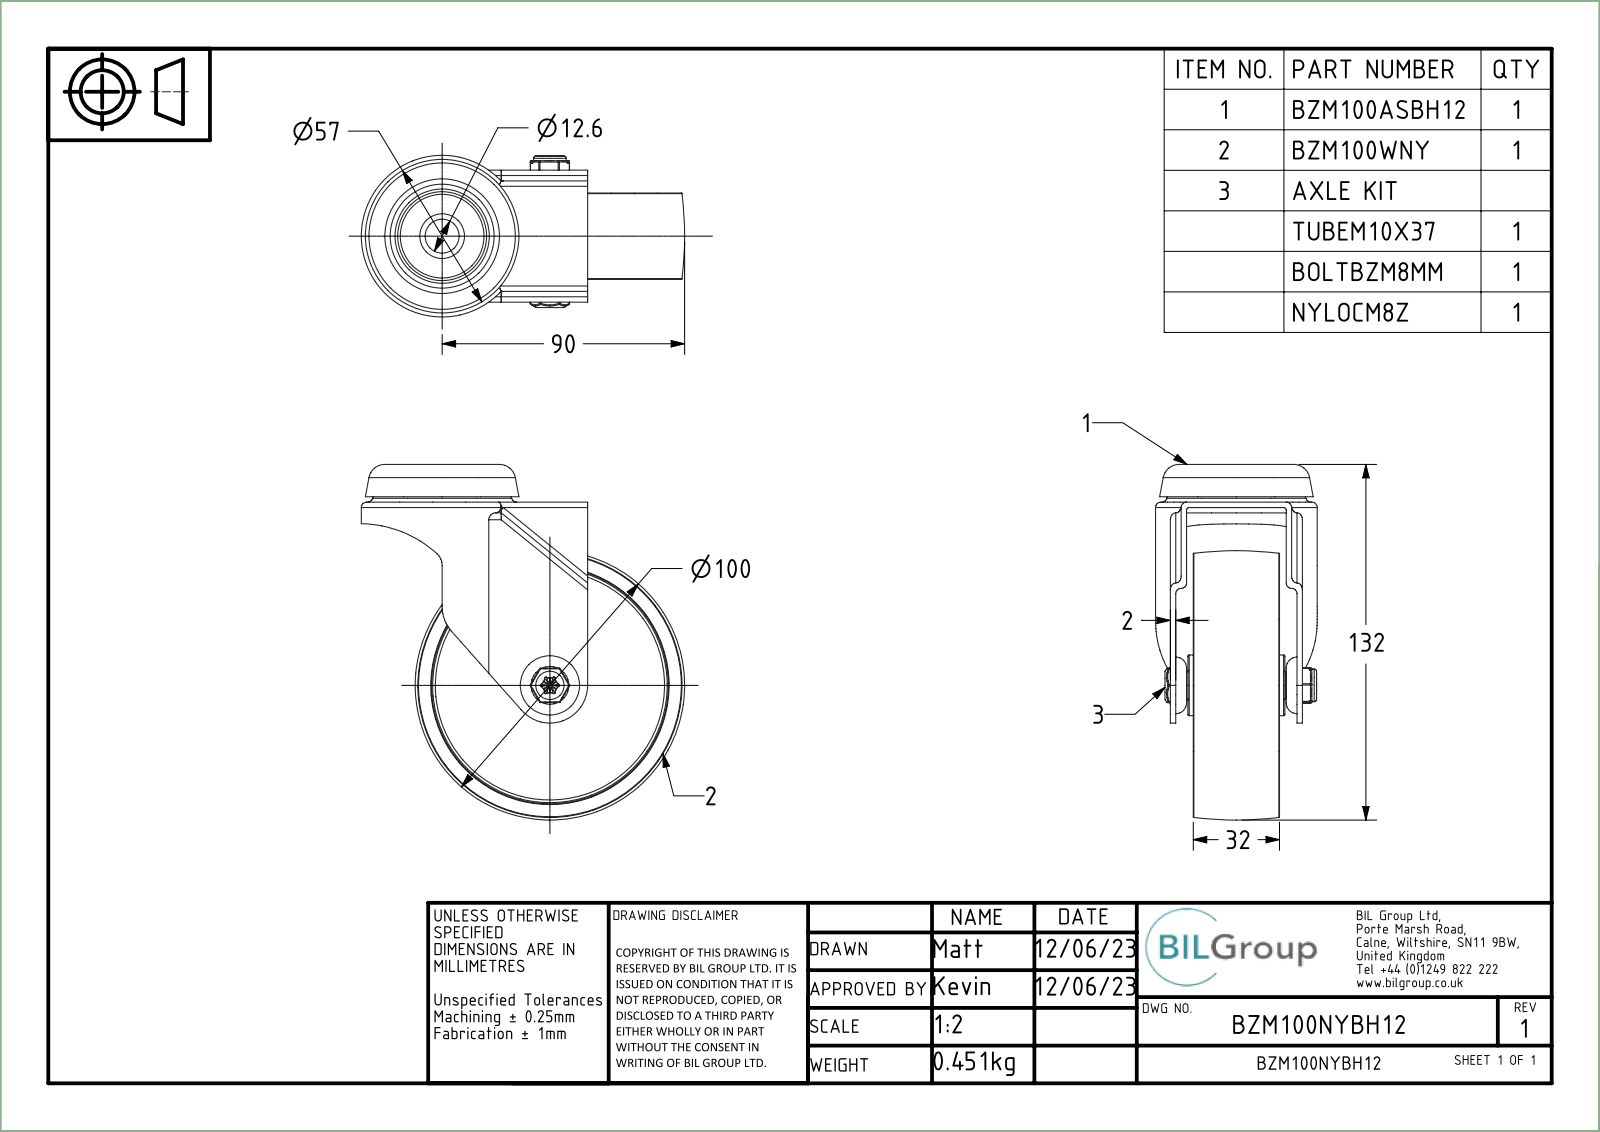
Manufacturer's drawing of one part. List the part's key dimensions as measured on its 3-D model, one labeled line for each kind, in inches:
Part name (STEP PRODUCT): BZM100ASBH12; ZINC PLATED PRESSED STEEL FORKS; ZINC PLATED PRESSED STEEL HEAD; BZM100NYBH12 (+8 more)
STEP written by: Spatial InterOp 3D (CONFIG_CONTROL_DESIGN)
Units: inches
Bodies: 7 solids, 396 faces (64 planar, 170 cylindrical, 162 other)
Overall size (bounding box): 5.197 × 4.724 × 2.362
Volume: 8.614 in³ · Surface area: 119.2 in²
Round holes (diameter × count): ⌀0.315 ×1, ⌀0.323 ×1, ⌀0.327 ×1, ⌀0.339 ×1, ⌀0.402 ×1, ⌀0.406 ×1, ⌀0.496 ×1
Round bosses / shafts (diameter × count): ⌀1.89 ×1, ⌀1.181 ×1, ⌀0.886 ×1, ⌀0.476 ×1, ⌀0.394 ×1, ⌀0.236 ×1
Partial cylindrical surfaces — rounded edges, fillets, slot ends (radius × count): R0.02 ×30, R0.079 ×22, R0.039 ×6, R0.551 ×2, R0.108 ×1, R0.236 ×1, R1.102 ×1, R1.181 ×1
Main face-to-face distances: 0.157, 0.079, 0.886, 0.807, 0.551, 1.043, 1.594, 0.709, 1.693, 0.256
